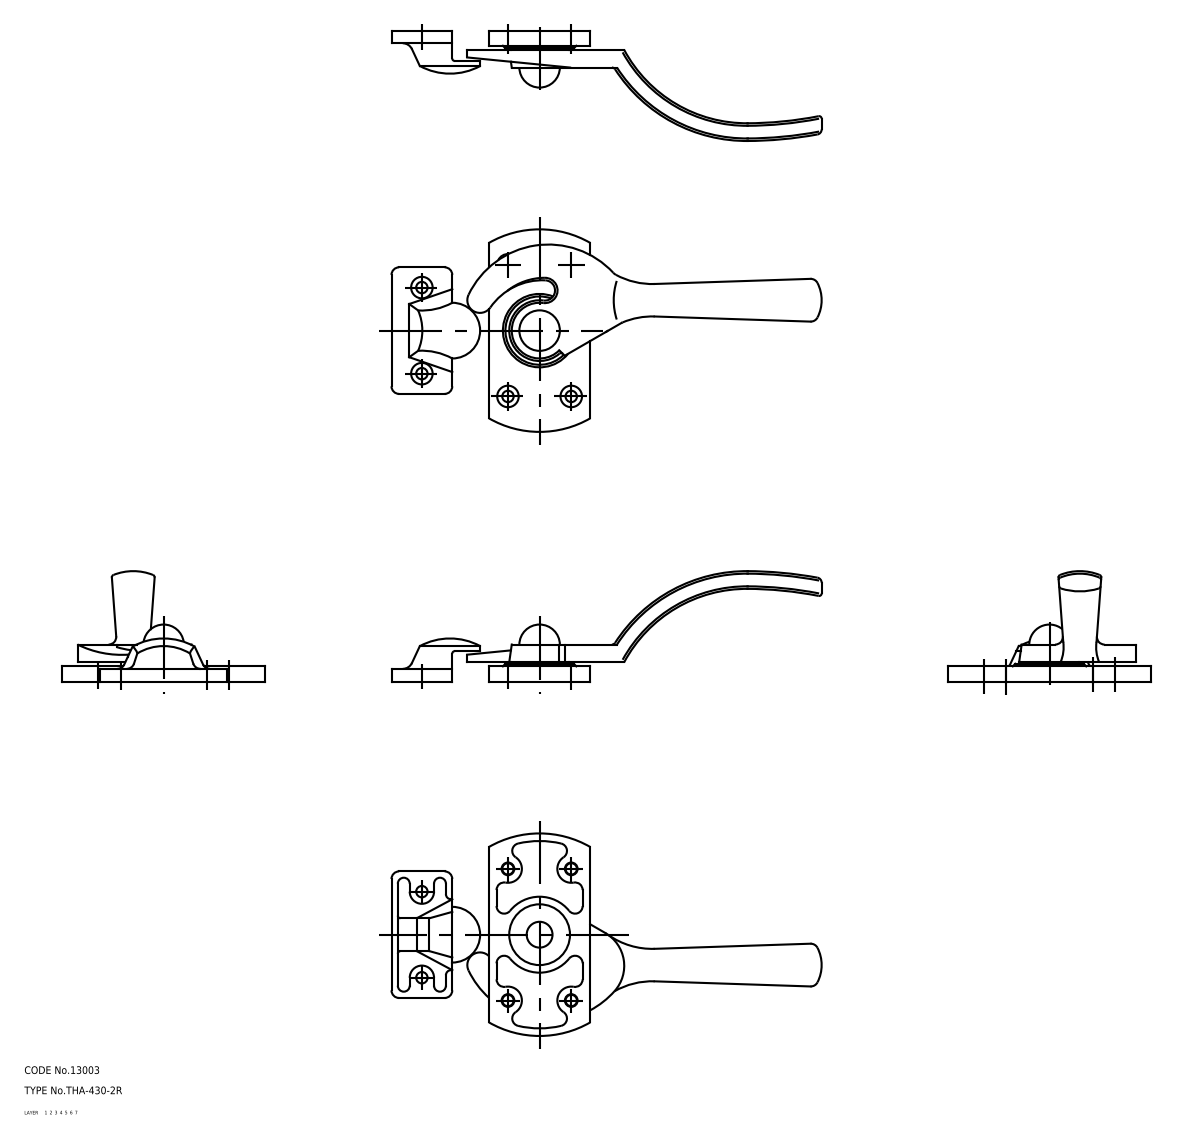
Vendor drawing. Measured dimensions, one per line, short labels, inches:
name: handle_mr; keeper_mr; washer_C_mr; washer_B_mr (+3 more)
written by: CADfix (AUTOMOTIVE_DESIGN)
unit: in
bodies: 6 solids, 168 faces (0 planar, 0 cylindrical, 168 other)
size: 6.689 × 3.15 × 1.718
volume: 2.399 in³; area: 35.94 in²
